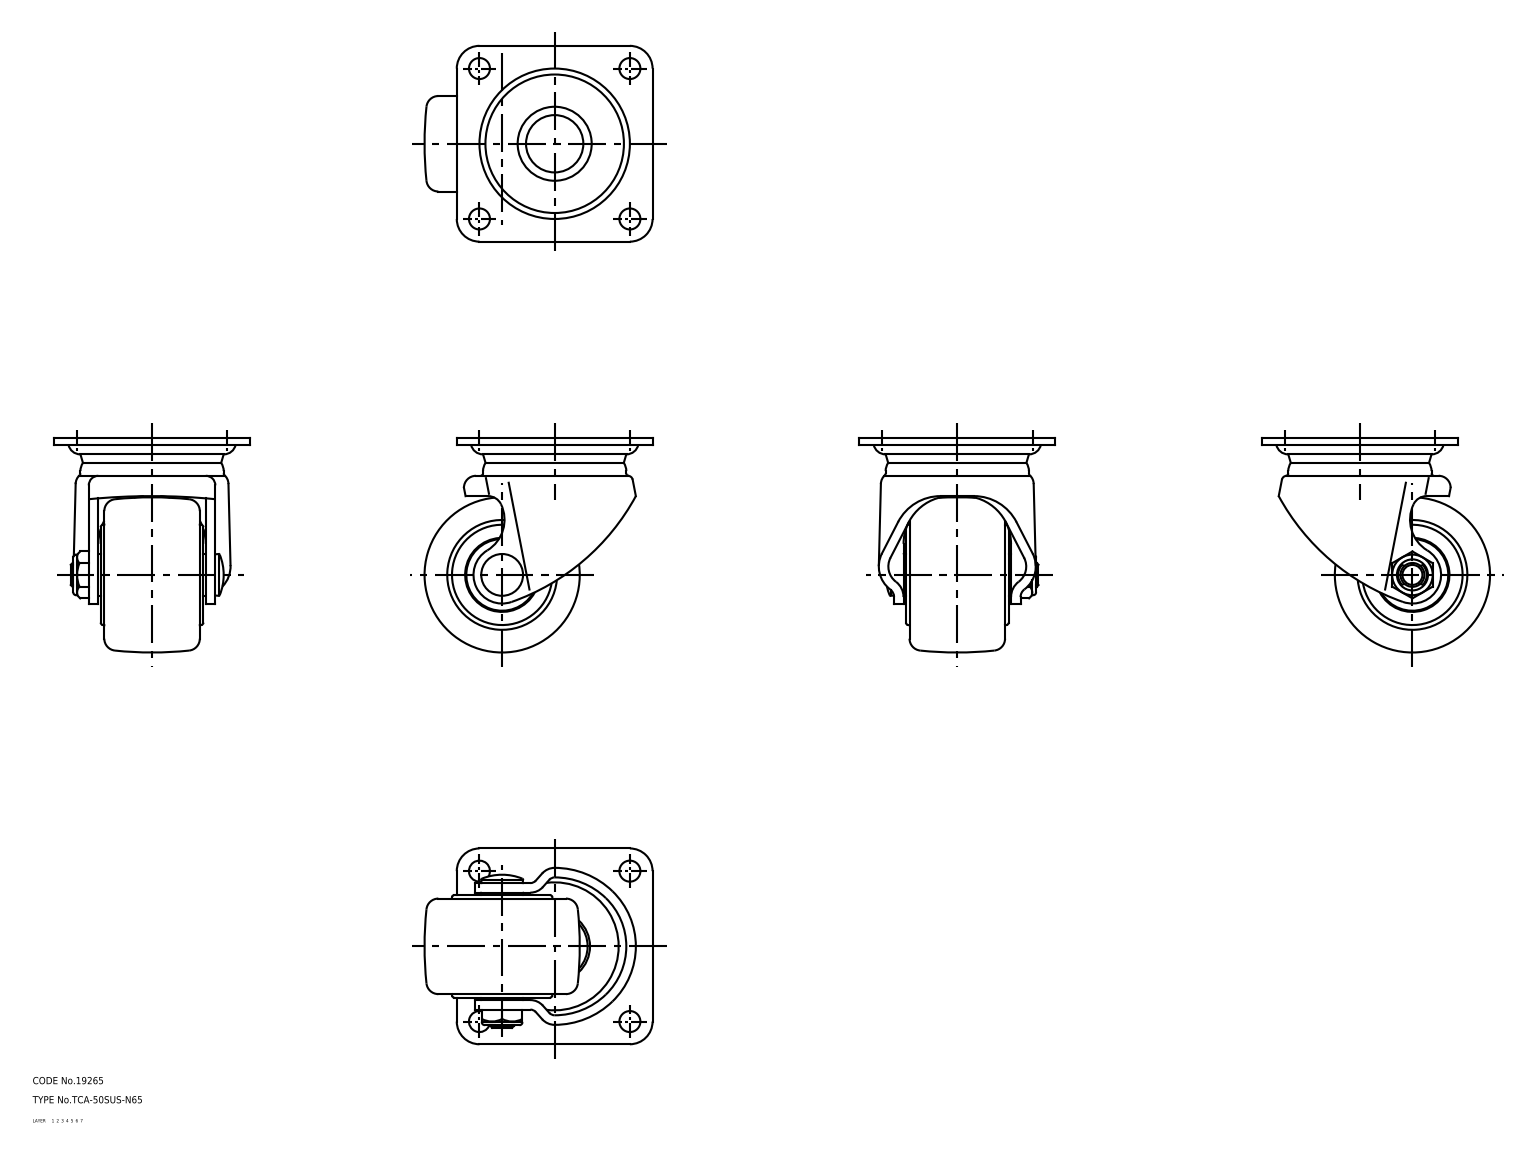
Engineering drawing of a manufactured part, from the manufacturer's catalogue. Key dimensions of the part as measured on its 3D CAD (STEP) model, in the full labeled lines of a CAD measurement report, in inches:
Part name (STEP PRODUCT): 67129632; 67129645; 67129658; 67129671 (+3 more)
STEP written by: CADfix (AUTOMOTIVE_DESIGN)
Units: inches
Bodies: 7 solids, 282 faces (0 planar, 0 cylindrical, 282 other)
Overall size (bounding box): 3.76 × 3.543 × 3.228
Volume: 13.77 in³ · Surface area: 98.36 in²
